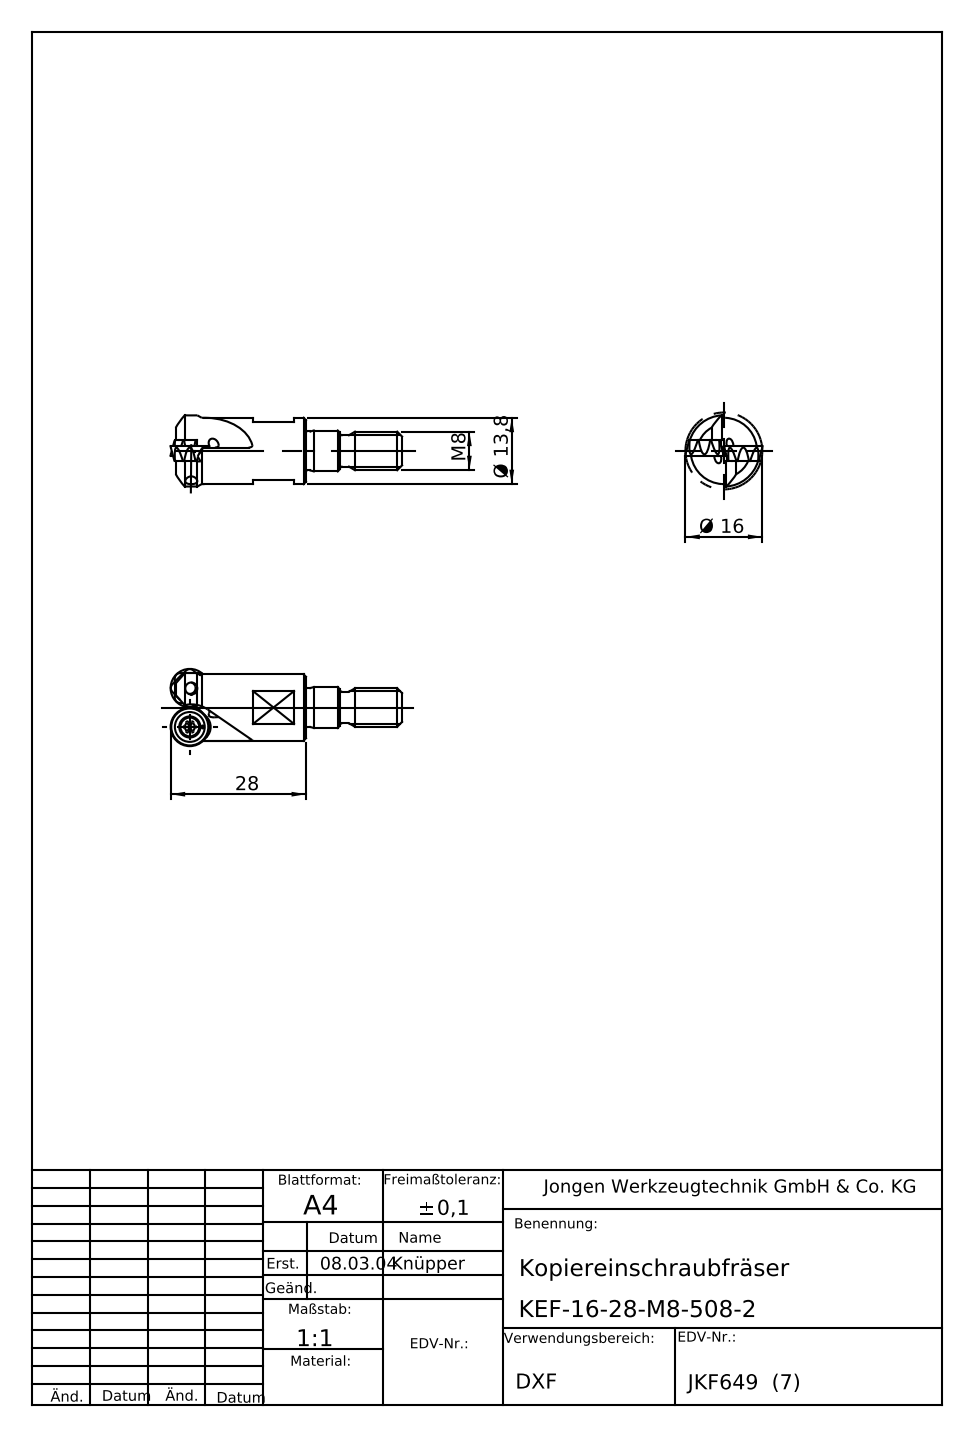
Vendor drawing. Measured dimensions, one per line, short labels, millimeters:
name: KEF_16_28_M8_508_2
written by: SolidWorks 2016 (AUTOMOTIVE_DESIGN)
unit: mm
bodies: 1 solid, 82 faces (22 planar, 28 cylindrical, 32 other)
size: 47.98 × 16 × 16
volume: 4 859 mm³; area: 2 389 mm²
holes: 2× ⌀2.1, 1× ⌀2
bosses: 1× ⌀13.8, 1× ⌀8.5, 1× ⌀8.1, 1× ⌀8, 1× ⌀6.5
rounds: 2× R0.5, 2× R6
face distances: 12, 5.3, 6.7, 1.4, 20, 22.5, 2.5, 31, 11, 8.5
